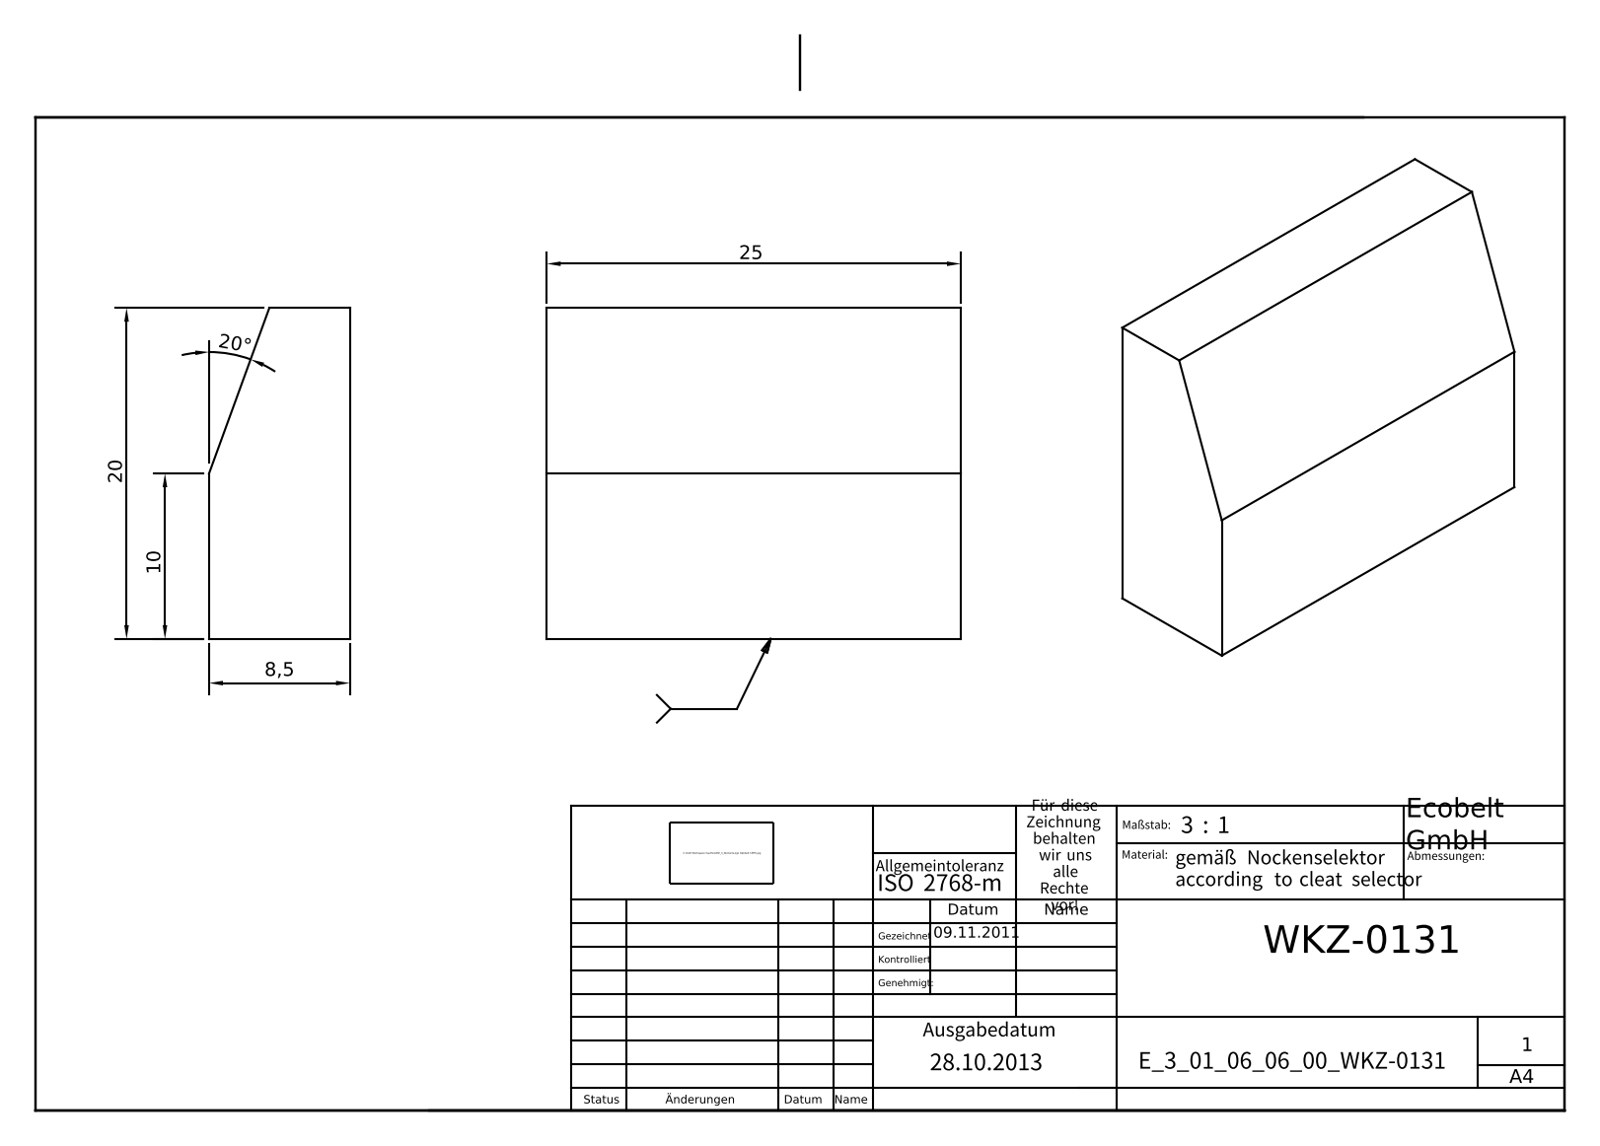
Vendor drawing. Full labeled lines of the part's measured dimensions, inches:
Part name (STEP PRODUCT): E_3_01_06_06_00_WKZ-0131
STEP written by: Autodesk Inventor 2025 (AUTOMOTIVE_DESIGN)
Units: inches
Bodies: 1 solid, 7 faces (7 planar, 0 cylindrical, 0 other)
Overall size (bounding box): 0.984 × 0.787 × 0.335
Volume: 0.232 in³ · Surface area: 2.564 in²
Main face-to-face distances: 0.335, 0.984, 0.787
